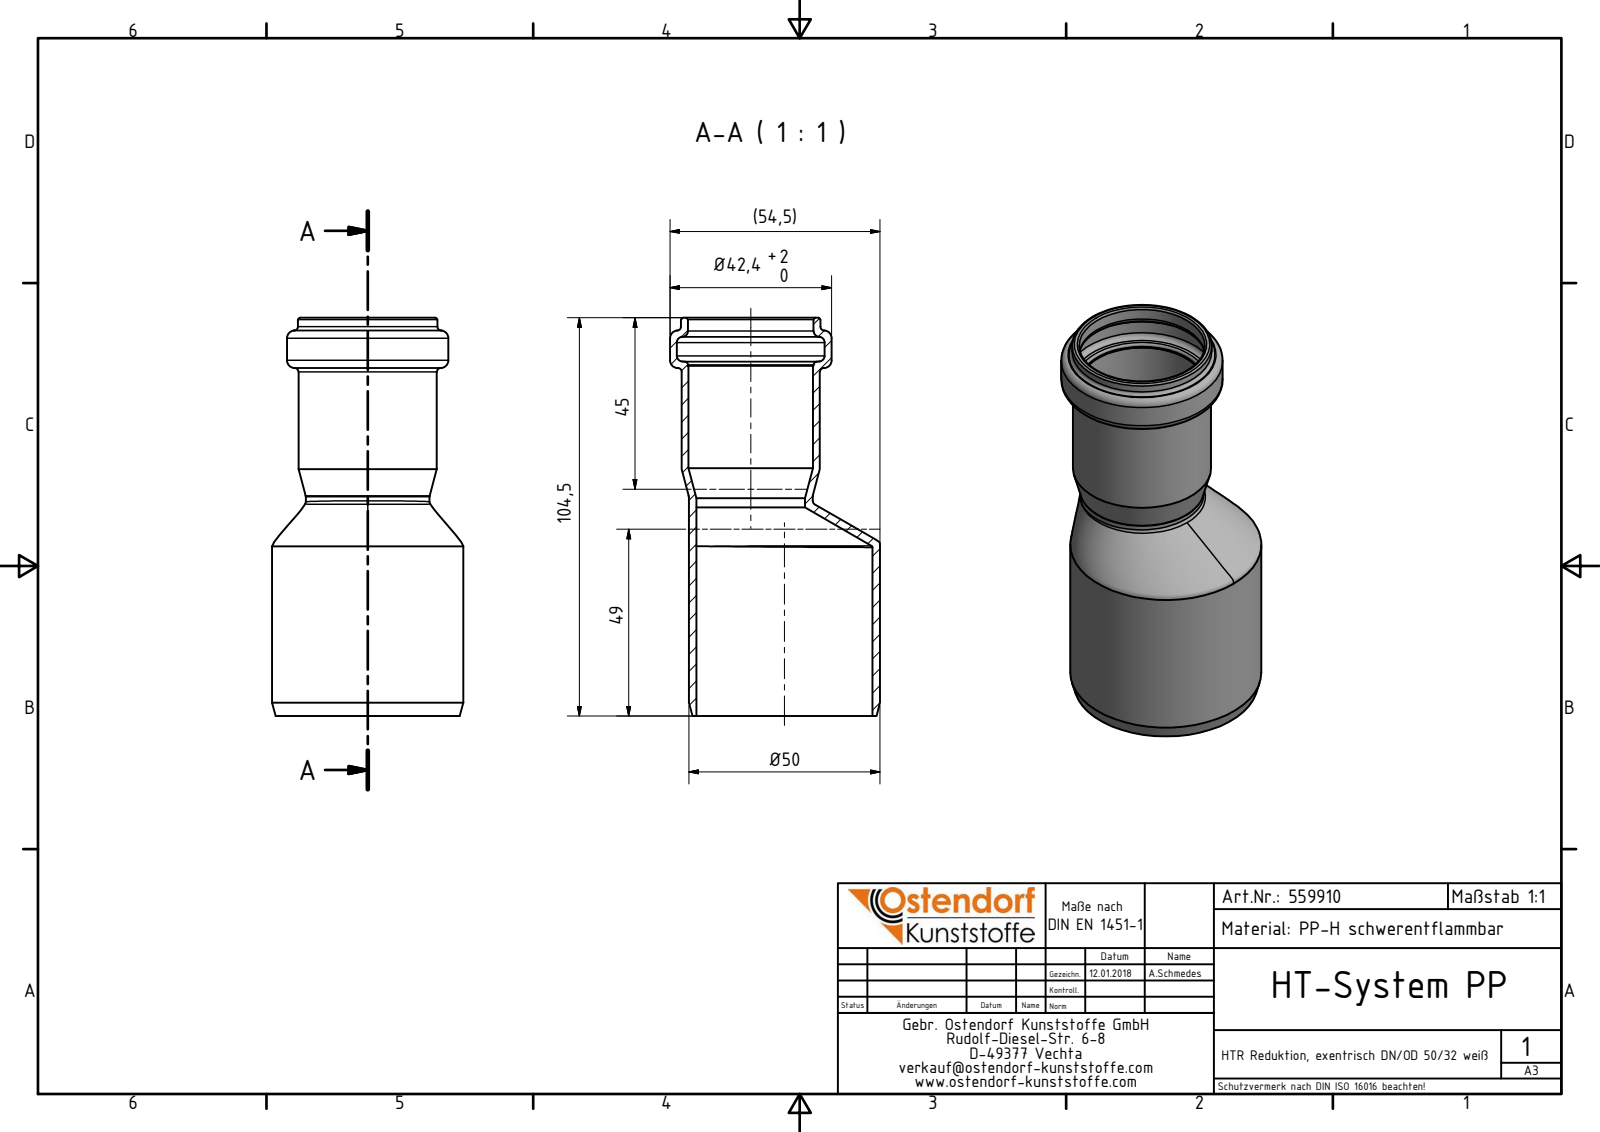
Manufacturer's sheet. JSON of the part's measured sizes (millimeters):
{"part_name": "559910 HTR DN_OD 50_32 weiß", "step_written_by": "Autodesk Inventor 2016 (AUTOMOTIVE_DESIGN)", "units": "millimeters", "bodies": {"solids": 1, "faces": 36, "planar": 3, "cylindrical": 11, "other": 22}, "overall_size": [104.5, 55.15, 50.2], "volume_mm3": 27789, "surface_area_mm2": 29191, "round_holes": [[28.5, 1], [32.7, 1], [33, 1], [38.8, 1], [46.2, 1]], "round_bosses_or_shafts": [[50.2, 1], [42.4, 1], [36.6, 1], [36.3, 1], [32.5, 1]], "face_to_face_distances": [104.5, 91.87, 12.63], "hole_center_spacings": [8.85]}
